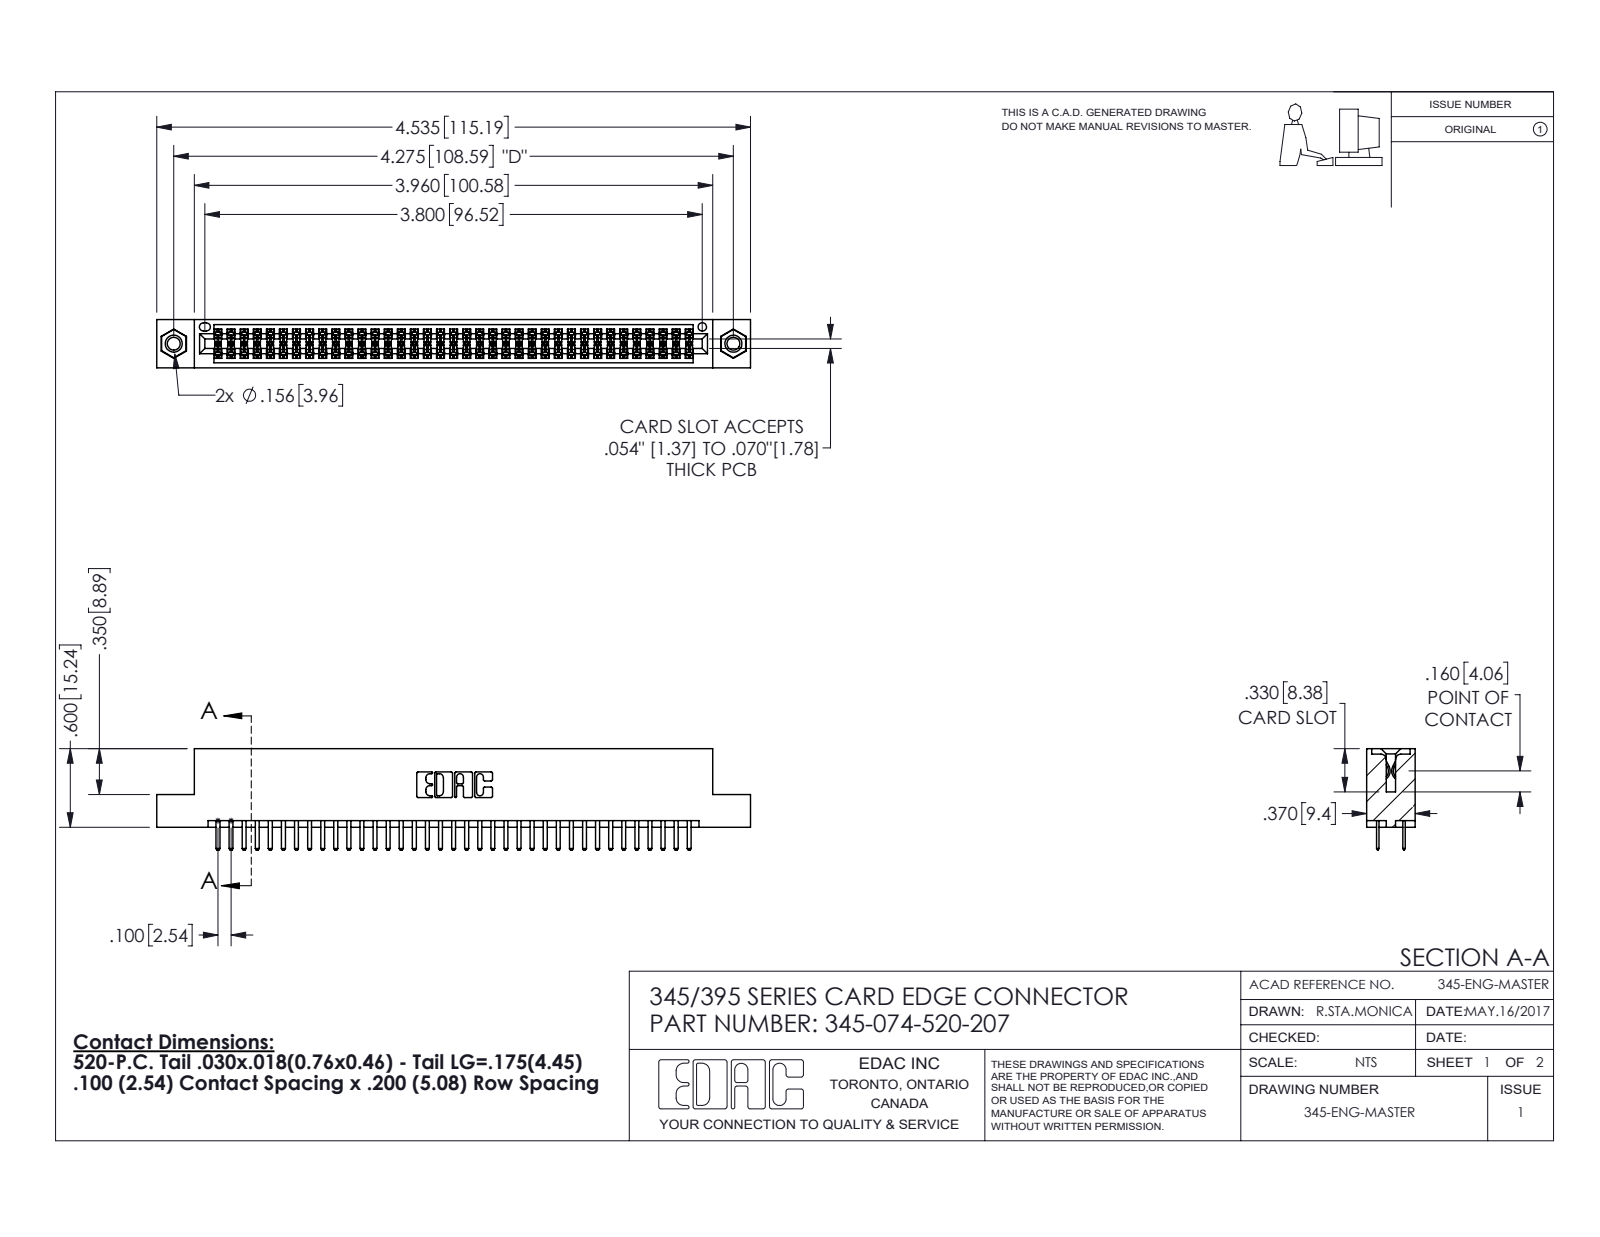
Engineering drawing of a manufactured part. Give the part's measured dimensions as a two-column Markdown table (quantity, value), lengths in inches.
| quantity | value |
| --- | --- |
| part name | 345-074-520-207; 345 Part_Flush Mounting Lugs - 0.156 Dia-TI; 345-292-001_345-293-120; 345-250-001_345-250-005-103 |
| STEP written by | SolidWorks 2016 (CONFIG_CONTROL_DESIGN) |
| units | inches |
| bodies | 77 solids, 4182 faces (2702 planar, 1464 cylindrical, 16 other) |
| overall size | 4.535 × 0.775 × 0.37 |
| volume | 0.677 in³ |
| surface area | 25.21 in² |
| round holes (diameter × count) | 0.098 × 2, 0.125 × 2, 0.156 × 2, 0.064 × 1 |
| round bosses / shafts (diameter × count) | 0.155 × 2 |
| partial cylindrical surfaces (radius × count) | 0.006 × 111, 0.01 × 78, 0.01 × 22, 0.007 × 6, 0.031 × 6, 0.026 × 3, 0.014 × 2, 0.019 × 2 |
| main face-to-face distances | 0.072, 0.298, 0.2, 0.37, 0.098, 0.272, 0.025, 0.225, 0.022, 0.072 |
| hole center spacings | 0.27, 4.039, 4.275 |
